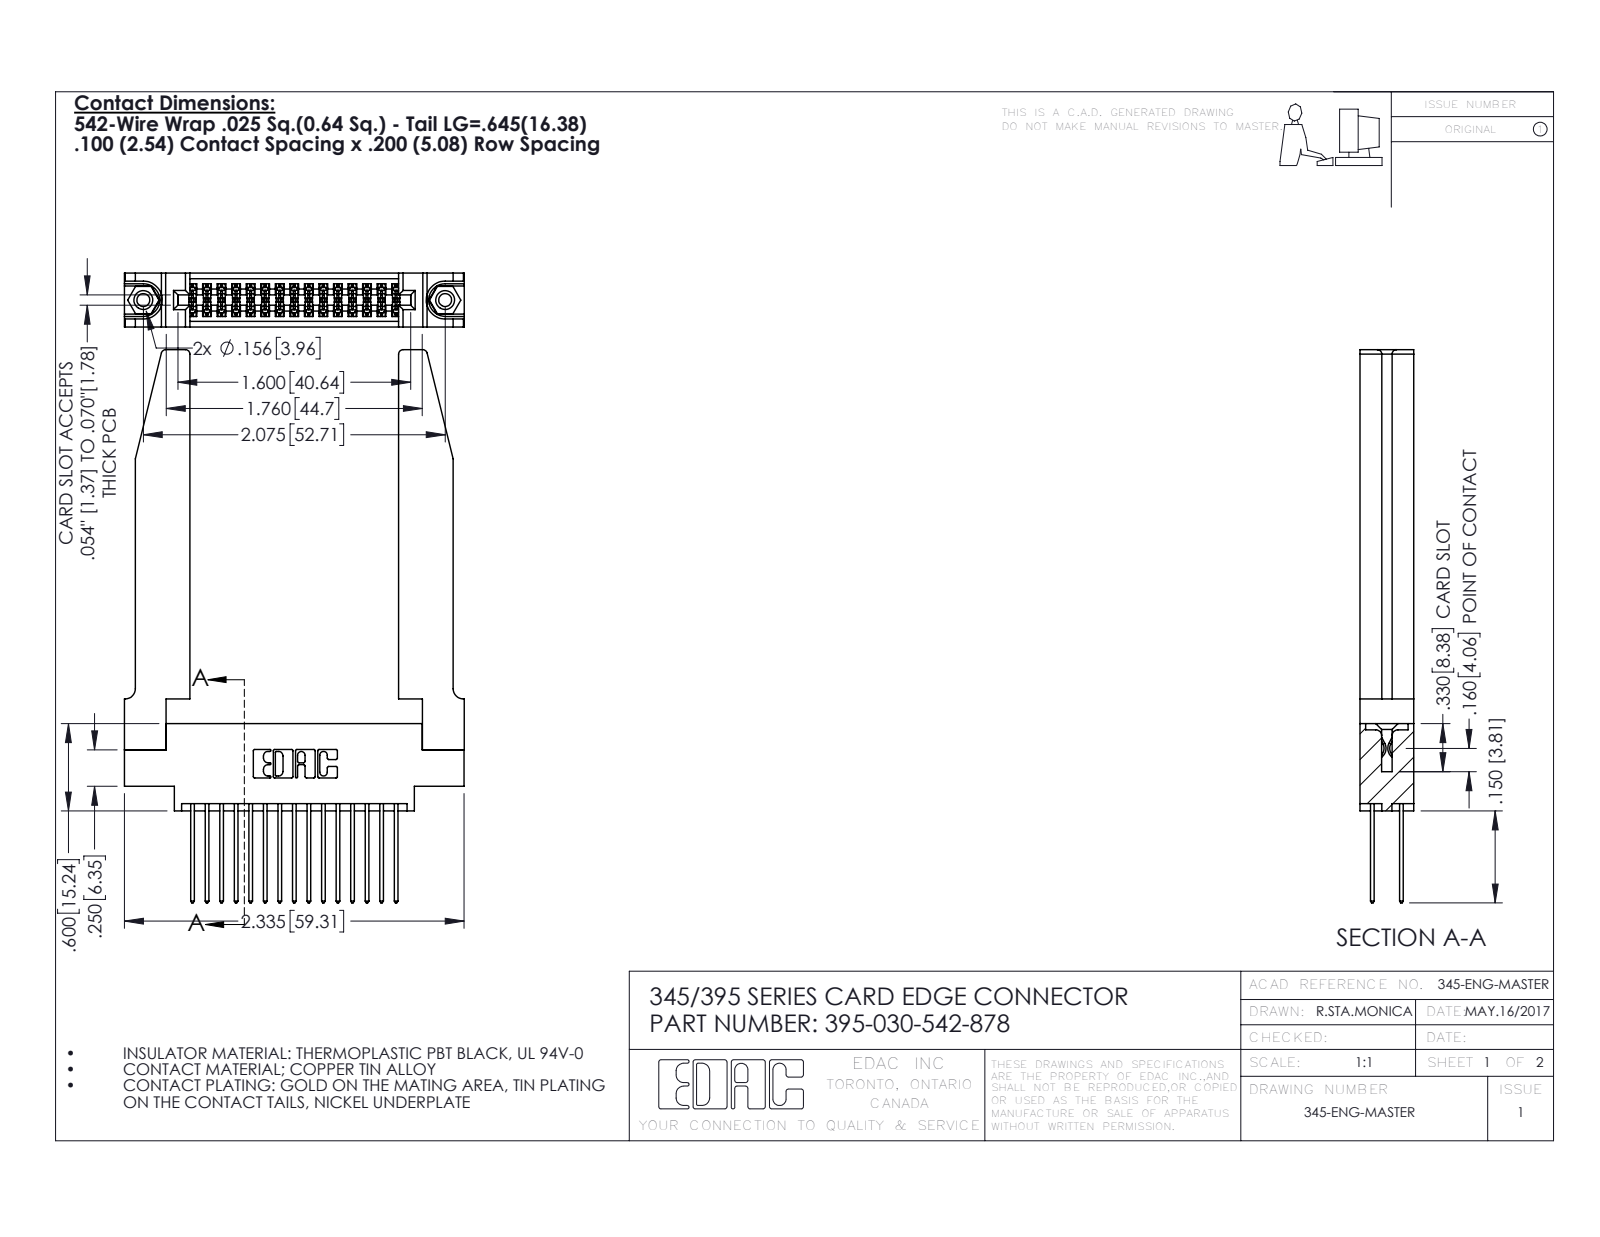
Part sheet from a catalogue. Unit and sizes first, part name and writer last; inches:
Units: inches
Overall size (bounding box): 3.802 × 2.336 × 0.37
Round holes (diameter × count): ⌀0.089 ×2, ⌀0.125 ×2, ⌀0.156 ×2, ⌀0.064 ×1
Round bosses / shafts (diameter × count): ⌀0.155 ×2
Partial cylindrical surfaces — rounded edges, fillets, slot ends (radius × count): R0.006 ×45, R0.01 ×30, R0.01 ×22, R0.03 ×8, R0.007 ×6, R0.031 ×6, R0.026 ×3, R0.014 ×2
Main face-to-face distances: 0.37, 0.072, 0.298, 0.098, 0.272, 0.025, 0.2, 0.225, 0.15, 0.148
Hole centre spacings: 0.27, 1.842, 2.075
Volume: 0.812 in³ · Surface area: 23.72 in²
Bodies: 35 solids, 1864 faces (1216 planar, 596 cylindrical, 52 other)
Part name (STEP PRODUCT): 345 Part_0.170 Offset - 0.156 Dia-TH; 395-030-542-878; 345-292-001_345-293-142; 345-220-078_345-220-078 (+1 more)
STEP written by: SolidWorks 2016 (CONFIG_CONTROL_DESIGN)
